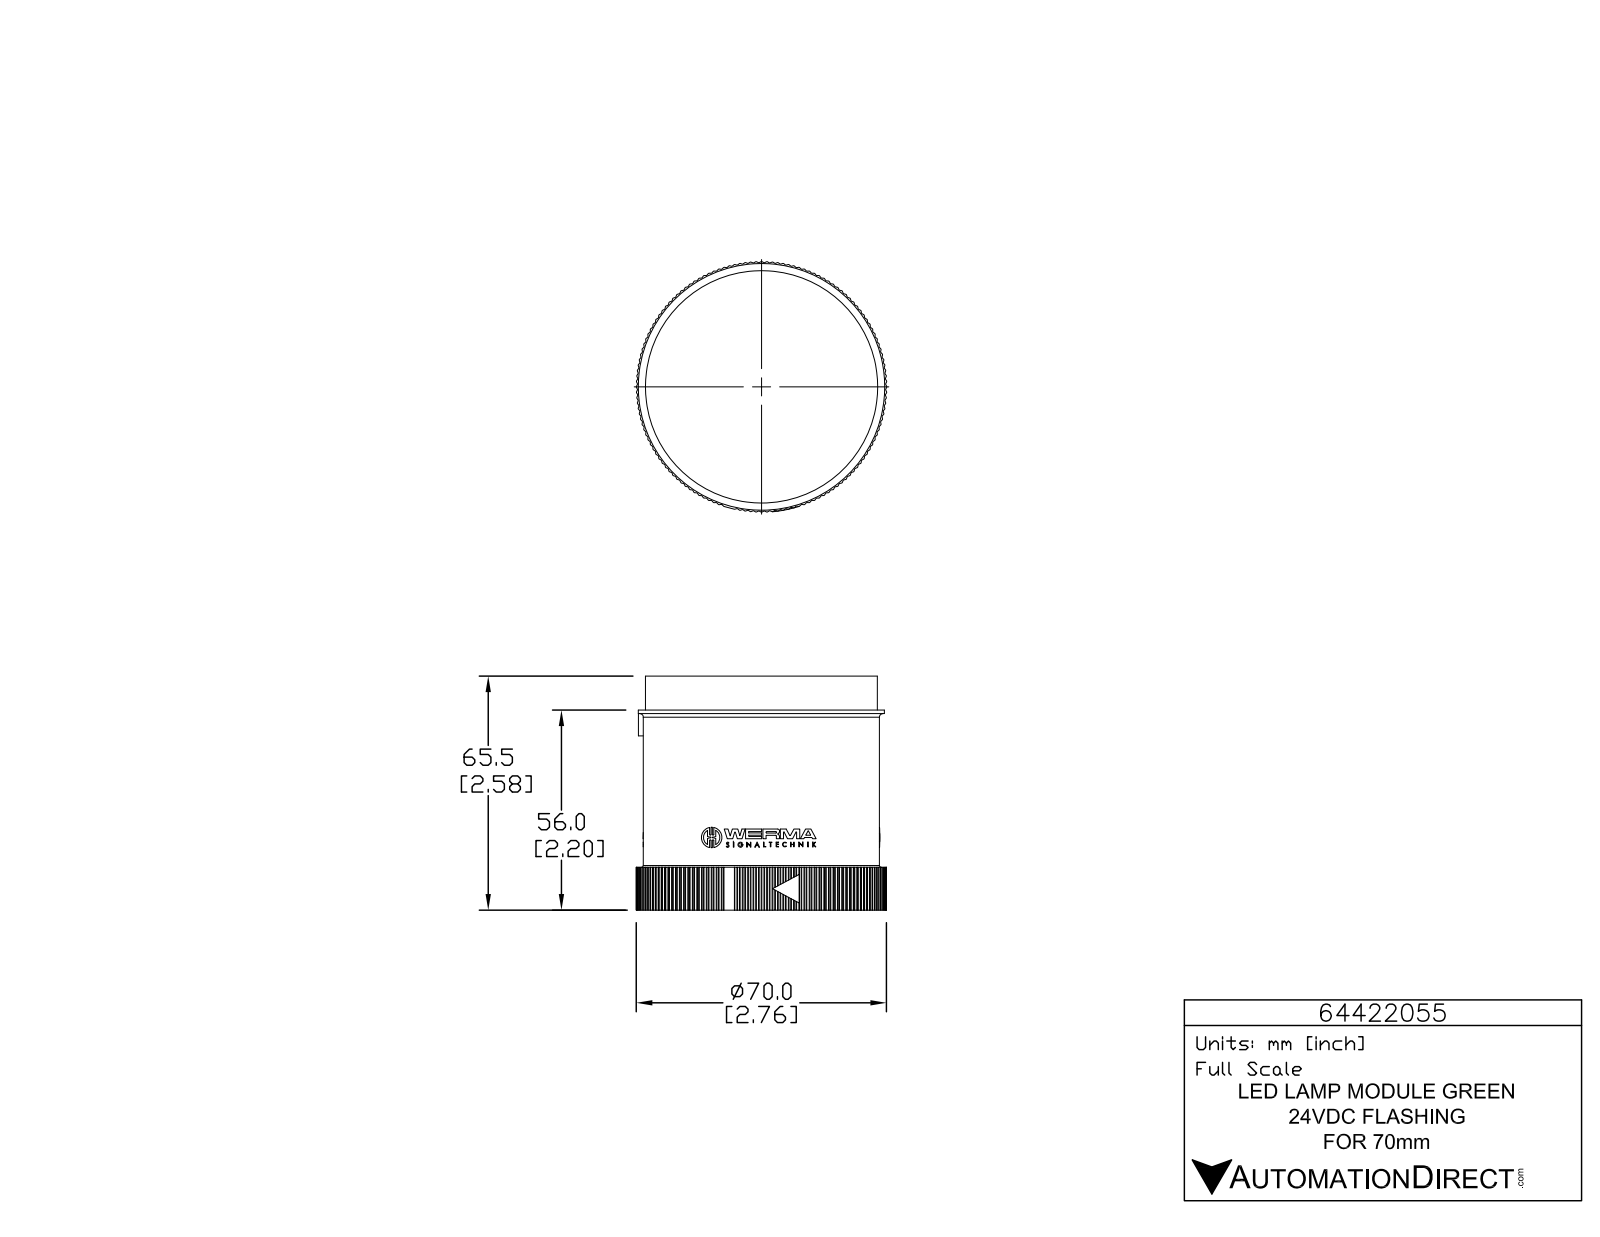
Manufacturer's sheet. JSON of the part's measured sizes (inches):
{"part_name": "64422055", "step_written_by": "SolidWorks 2015 (AUTOMOTIVE_DESIGN)", "units": "inches", "bodies": {"solids": 1, "faces": 1400, "planar": 832, "cylindrical": 563, "other": 5}, "overall_size": [2.762, 2.762, 2.579], "volume_in3": 12.02, "surface_area_in2": 37.48, "round_holes": [[0.039, 3], [2.575, 1]], "round_bosses_or_shafts": [[0.226, 3], [0.056, 3], [2.717, 1], [2.606, 1], [2.559, 1]], "partial_cylinders_radius": [[0.008, 285], [0.008, 6], [0.008, 6], [0.008, 6], [0.131, 6], [0.004, 3], [0.005, 3], [0.008, 3]], "face_to_face_distances": [2.201, 2.451, 0.378, 2.579, 2.205, 1.827, 0.374, 2.452, 0.472, 0.094]}
